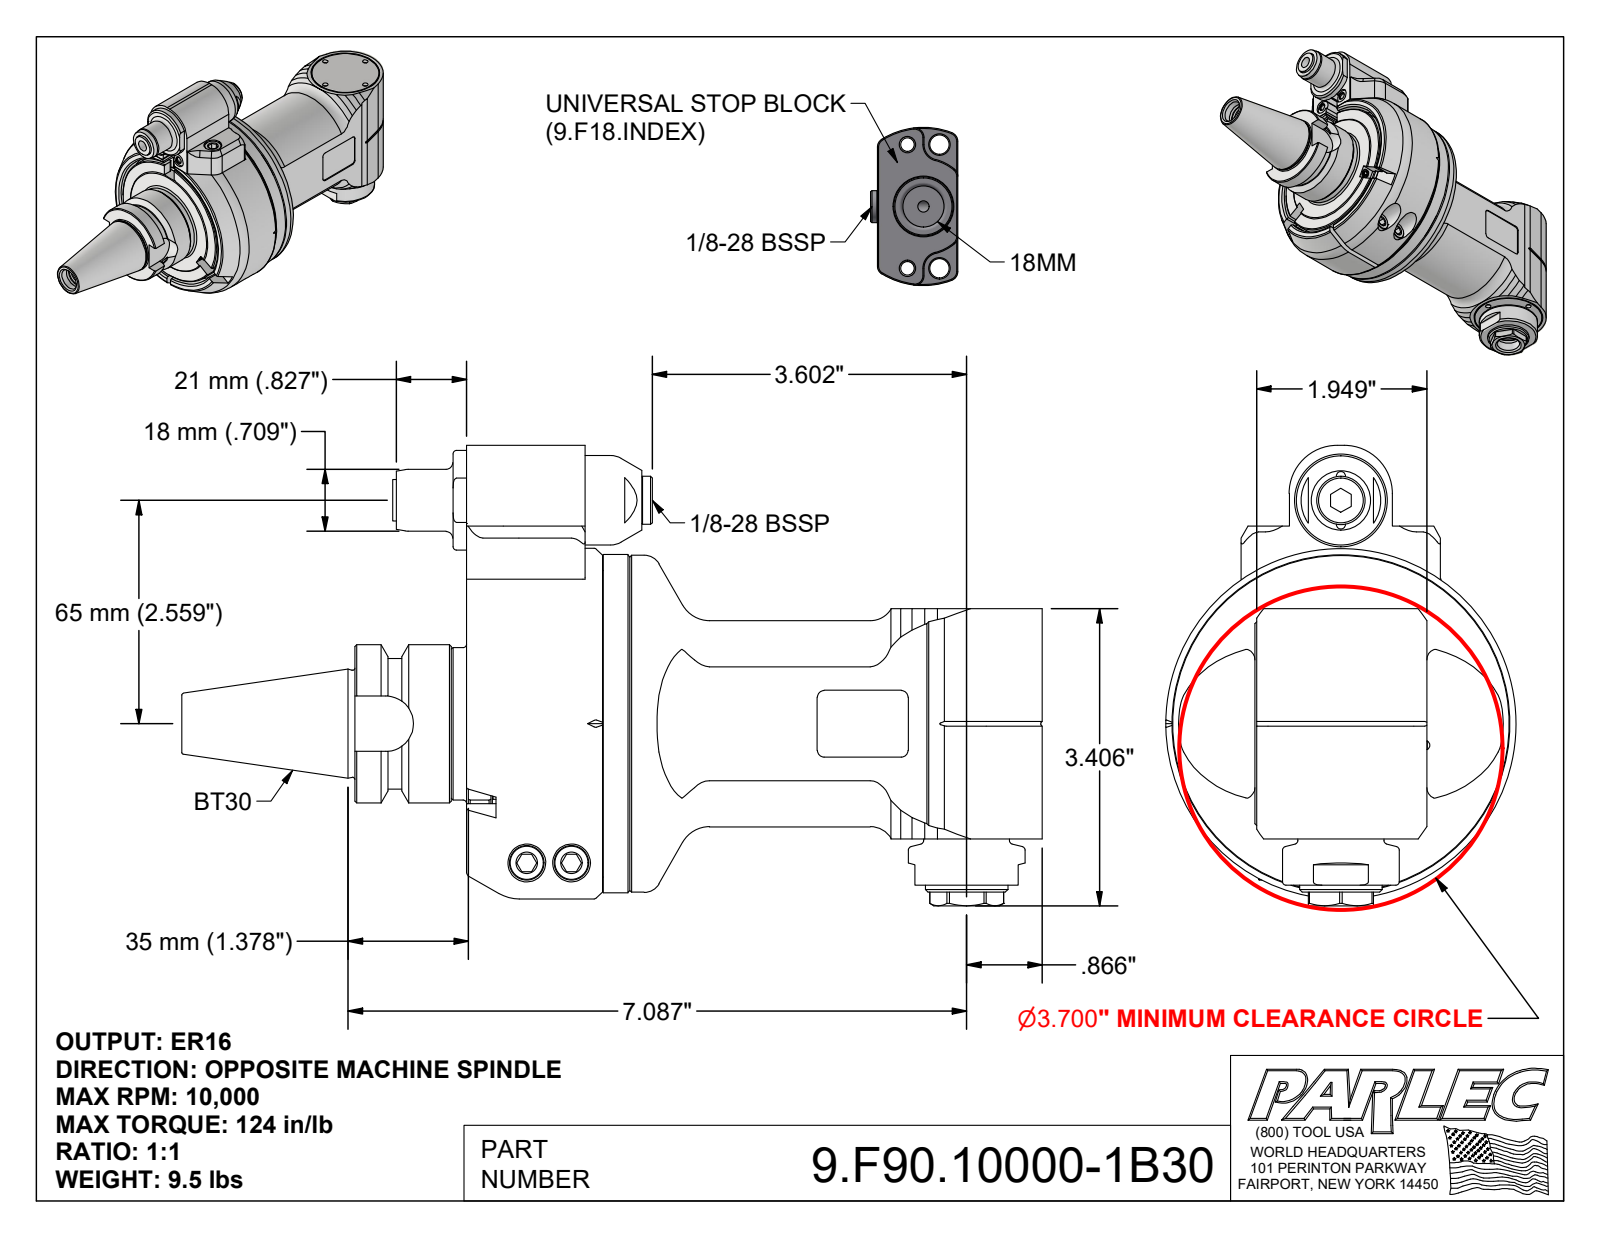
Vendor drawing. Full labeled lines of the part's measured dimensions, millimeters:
Part name (STEP PRODUCT): 9.F90.10000-1B30; step_9ga11c_336 (EVO, Type 1, BT30, 65mm); 9_F90_10000
STEP written by: Autodesk Inventor 2022 (AUTOMOTIVE_DESIGN)
Units: millimetres
Bodies: 26 solids, 872 faces (337 planar, 248 cylindrical, 287 other)
Overall size (bounding box): 250.4 × 134 × 102
Volume: 832 300 mm³ · Surface area: 168 500 mm²
Round holes (diameter × count): ⌀8.5 ×20, ⌀3.2 ×8, ⌀5 ×7, ⌀4.2 ×6, ⌀1.6 ×4, ⌀2 ×4, ⌀3.3 ×4, ⌀6 ×3, ⌀6.5 ×3, ⌀8 ×3, ⌀11 ×3, ⌀13 ×3
Round bosses / shafts (diameter × count): ⌀10 ×5, ⌀6 ×4, ⌀4 ×4, ⌀22 ×2, ⌀18 ×2, ⌀5 ×2, ⌀2.5 ×2, ⌀102 ×1
Partial cylindrical surfaces — rounded edges, fillets, slot ends (radius × count): R1 ×14, R2 ×12, R3 ×6, R4 ×4, R0.4 ×2, R0.5 ×2, R8 ×2, R14 ×2
Main face-to-face distances: 8.5, 0.5, 7, 39.5, 32, 7.5, 1, 16.5, 32.5, 5
Hole centre spacings: 38.5, 29, 37.1, 41.5, 46.5, 76.3, 16.5, 46.3
